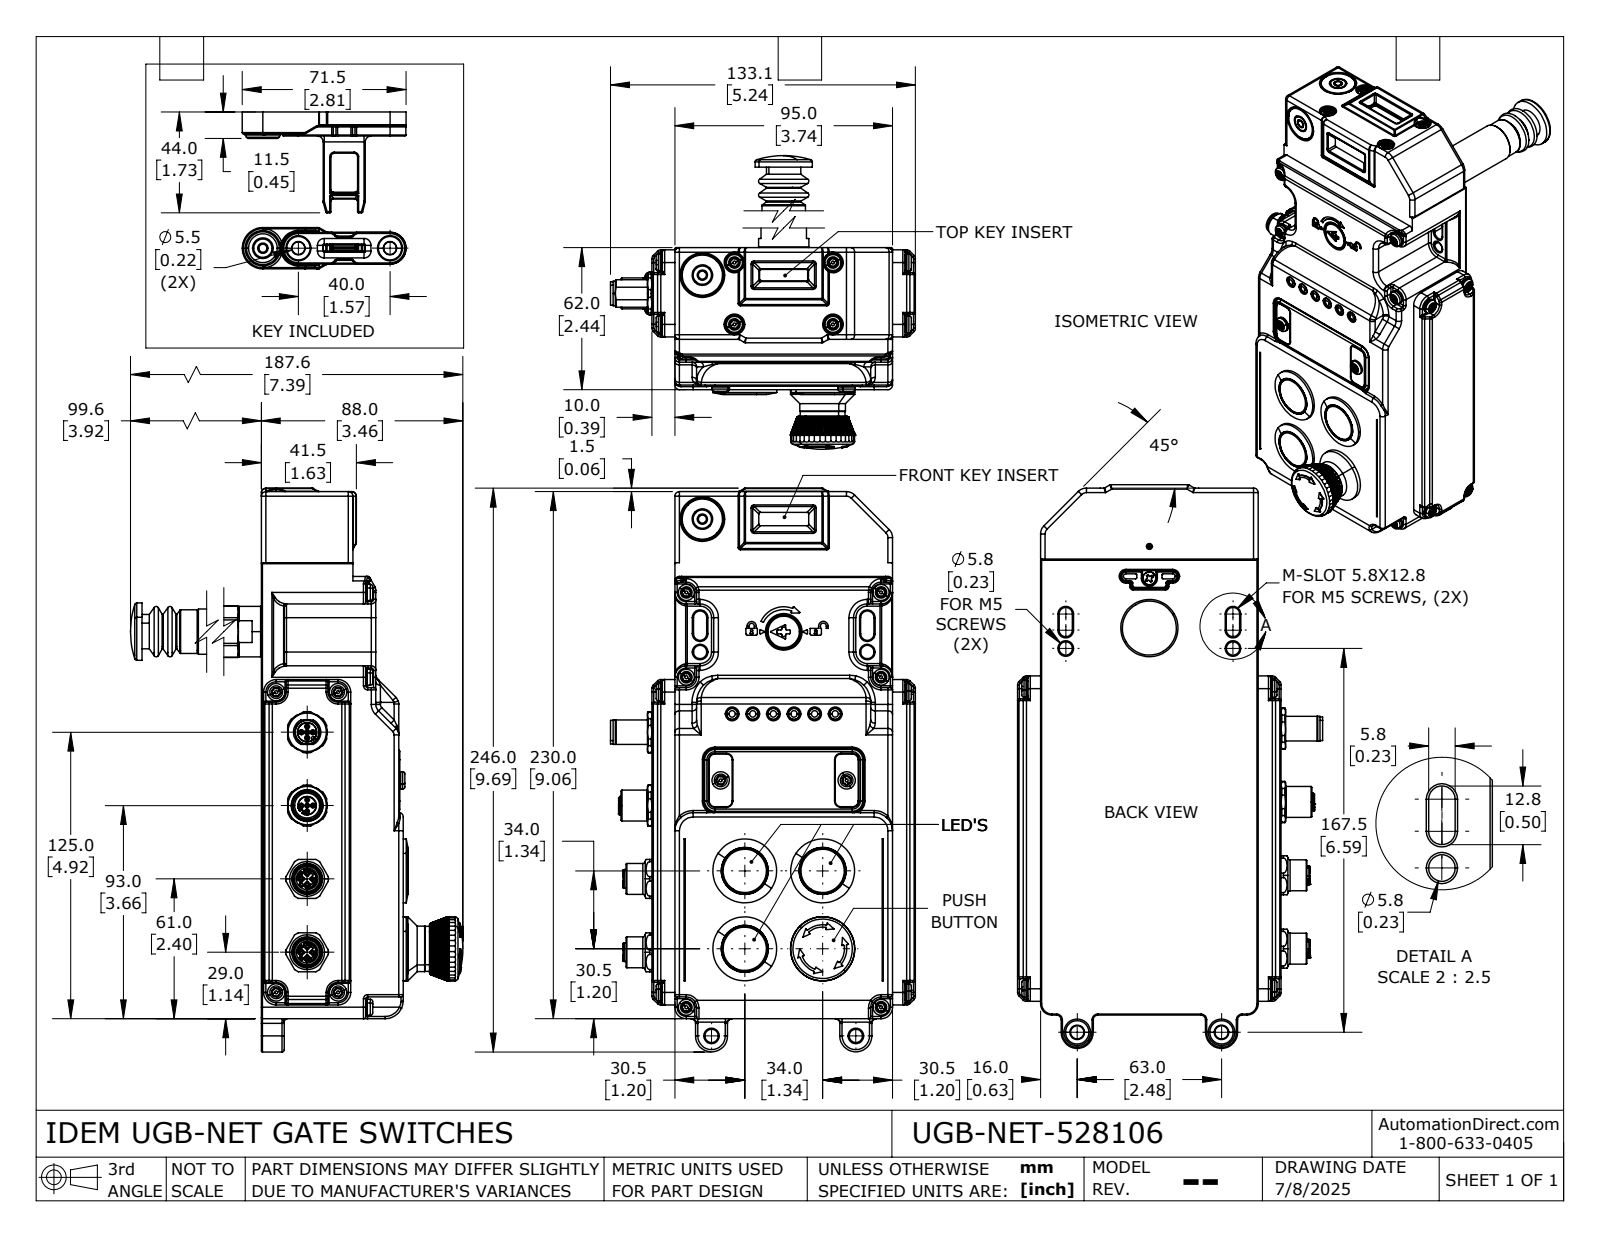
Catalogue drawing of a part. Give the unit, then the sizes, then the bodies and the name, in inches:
Units: inches
Overall size (bounding box): 10.217 × 7.386 × 5.24
Round holes (diameter × count): ⌀0.177 ×14, ⌀0.049 ×8, ⌀0.077 ×8, ⌀0.157 ×8, ⌀0.315 ×8, ⌀0.087 ×7, ⌀0.197 ×6, ⌀0.043 ×5, ⌀0.098 ×4, ⌀0.228 ×4, ⌀0.789 ×3, ⌀0.138 ×2
Round bosses / shafts (diameter × count): ⌀0.051 ×16, ⌀0.276 ×10, ⌀0.138 ×10, ⌀0.189 ×8, ⌀0.039 ×7, ⌀0.299 ×6, ⌀0.244 ×6, ⌀0.079 ×5
Partial cylindrical surfaces — rounded edges, fillets, slot ends (radius × count): R0.039 ×224, R0.02 ×177, R0.008 ×129, R0.079 ×72, R0.031 ×47, R0.012 ×44, R0.016 ×14, R0.098 ×14
Main face-to-face distances: 0.394, 4.134, 2.441, 0.472, 3.74, 1.535, 0.079, 0.059, 0.039, 4.528
Hole centre spacings: 0.098, 0.139, 0.197, 1.063, 1.264, 1.26, 2.52, 2.522
Volume: 80.92 in³ · Surface area: 196.2 in²
Bodies: 7 solids, 4637 faces (1382 planar, 1710 cylindrical, 1545 other)
Part name (STEP PRODUCT): UGB-NET-528106
STEP written by: SolidWorks 2024 (AUTOMOTIVE_DESIGN)
